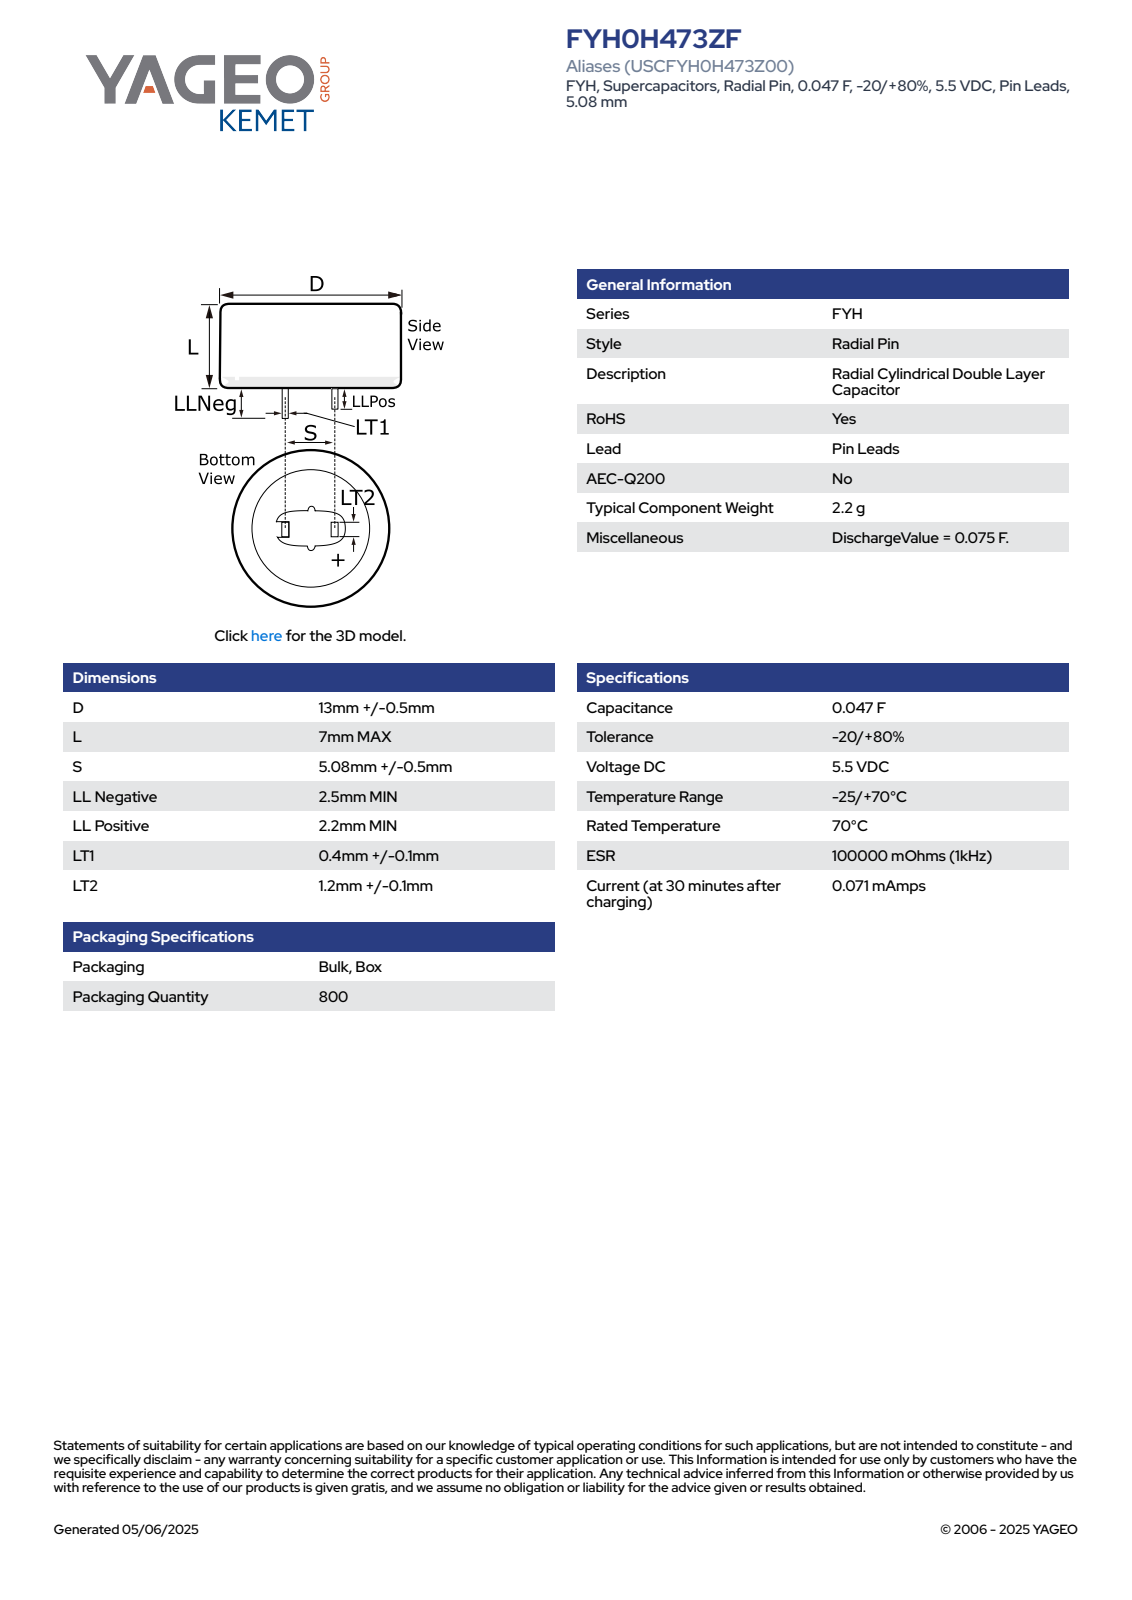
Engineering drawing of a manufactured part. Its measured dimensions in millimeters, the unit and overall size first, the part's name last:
Units: millimetres
Overall size (bounding box): 13.5 × 13.5 × 9.5
Round bosses / shafts (diameter × count): ⌀13.5 ×1
Partial cylindrical surfaces — rounded edges, fillets, slot ends (radius × count): R6.76 ×1
Main face-to-face distances: 7, 0.5, 5.08, 5.58, 4.58, 1.3, 2.2, 9.2, 2.5, 9.5
Volume: 1 001 mm³ · Surface area: 584 mm²
Bodies: 1 solid, 78 faces (70 planar, 4 cylindrical, 4 other)
Part name (STEP PRODUCT): CDR_LPLLN_D13.5L7S5.08LLNEG2.5LLPOS2.2LT10.5LT21.3
STEP written by: SolidWorks 2014 (AUTOMOTIVE_DESIGN)
